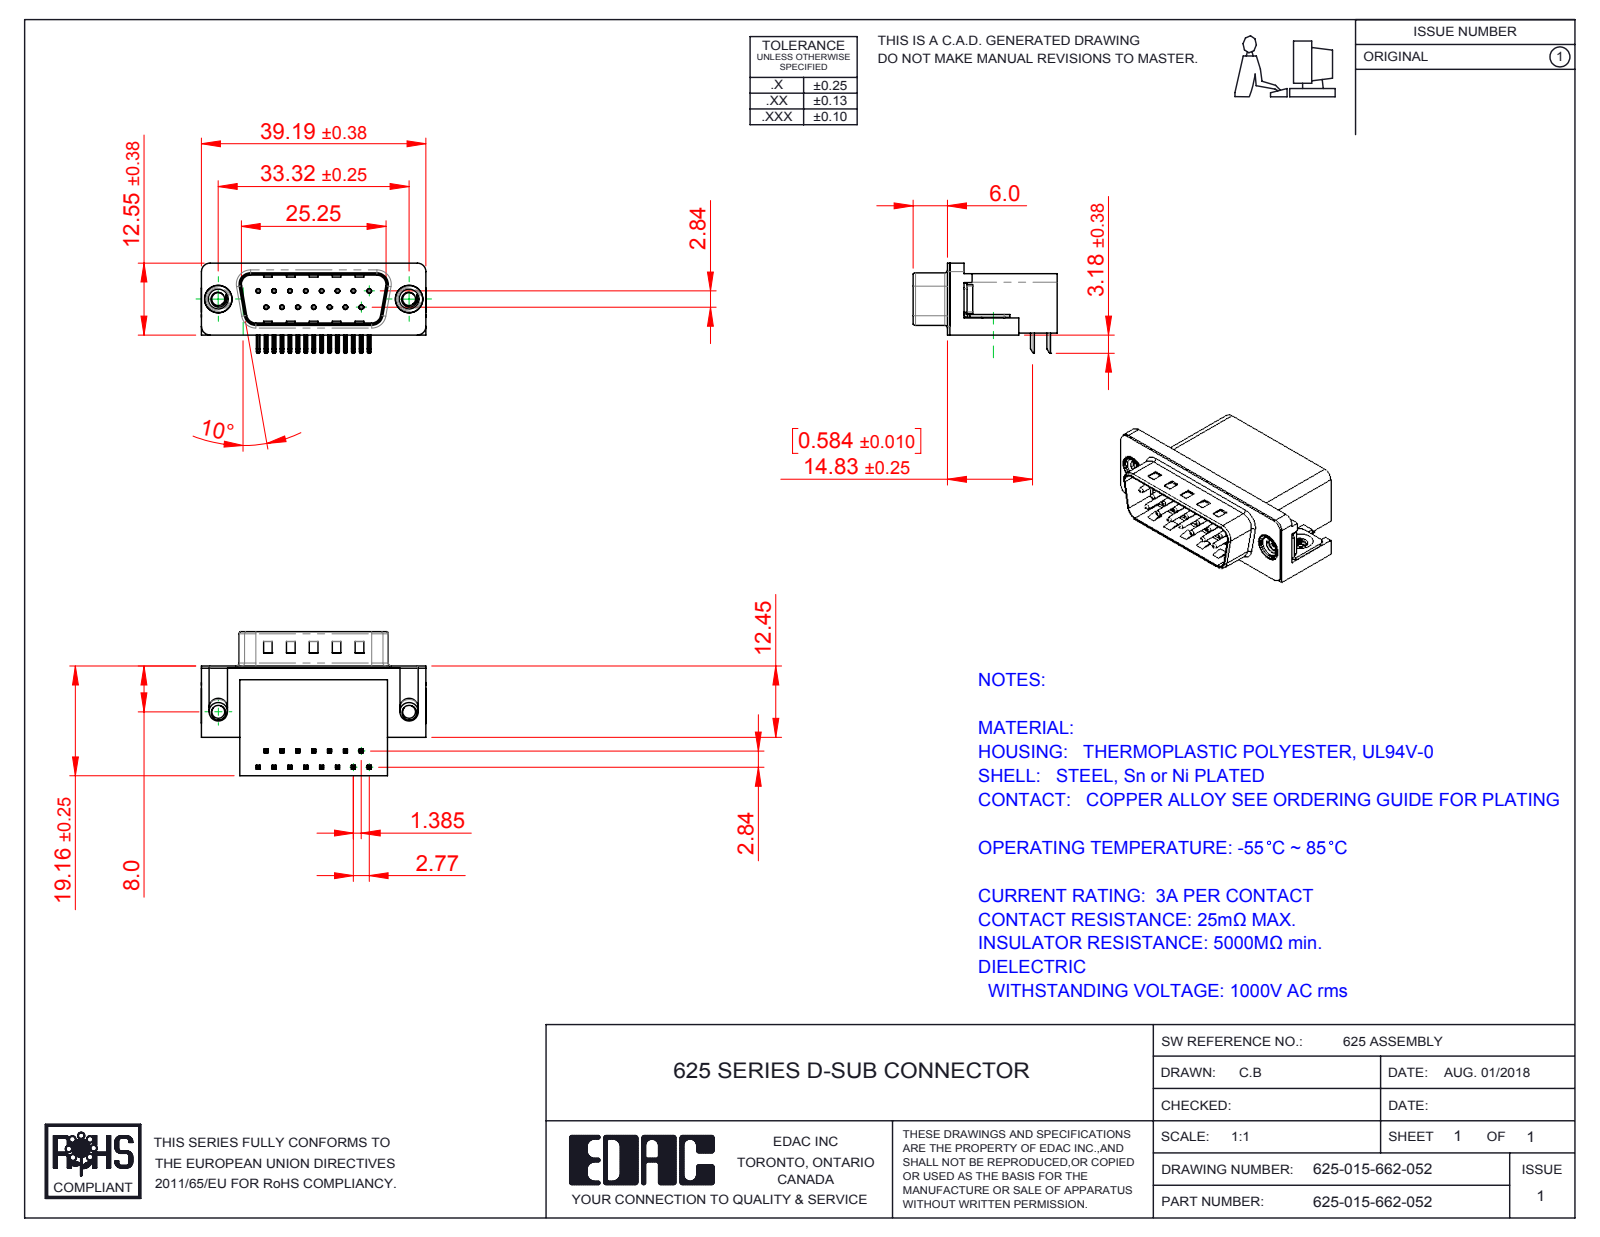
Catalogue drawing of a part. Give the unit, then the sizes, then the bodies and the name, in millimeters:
Units: millimetres
Overall size (bounding box): 39.22 × 25.16 × 15.73
Round holes (diameter × count): ⌀0.35 ×15, ⌀0.8 ×15, ⌀2.26 ×4, ⌀4 ×2, ⌀4.8 ×2, ⌀5 ×2
Round bosses / shafts (diameter × count): ⌀0.75 ×15, ⌀4.9 ×2, ⌀4.75 ×2, ⌀3.9 ×2, ⌀3.26 ×2
Partial cylindrical surfaces — rounded edges, fillets, slot ends (radius × count): R0.25 ×68, R0.12 ×30, R1 ×16, R0.5 ×9, R1.6 ×8, R1.5 ×6, R0.9 ×4, R2 ×4
Main face-to-face distances: 0.4, 10.35, 18.76, 2.1, 10.46, 19.16, 1.7, 10.86, 8.76, 16.26
Hole centre spacings: 3.16, 2.77, 5.54, 8.31, 11.08, 5.03, 5.04, 7.48
Volume: 6 255 mm³ · Surface area: 6 504 mm²
Bodies: 21 solids, 1511 faces (895 planar, 459 cylindrical, 157 other)
Part name (STEP PRODUCT): 625 Contact Top; 625 Shell_15 Socket; 625 4-40 Threaded Rivet; 625 Contact Bottom (+3 more)
STEP written by: SolidWorks 2016 (CONFIG_CONTROL_DESIGN)
